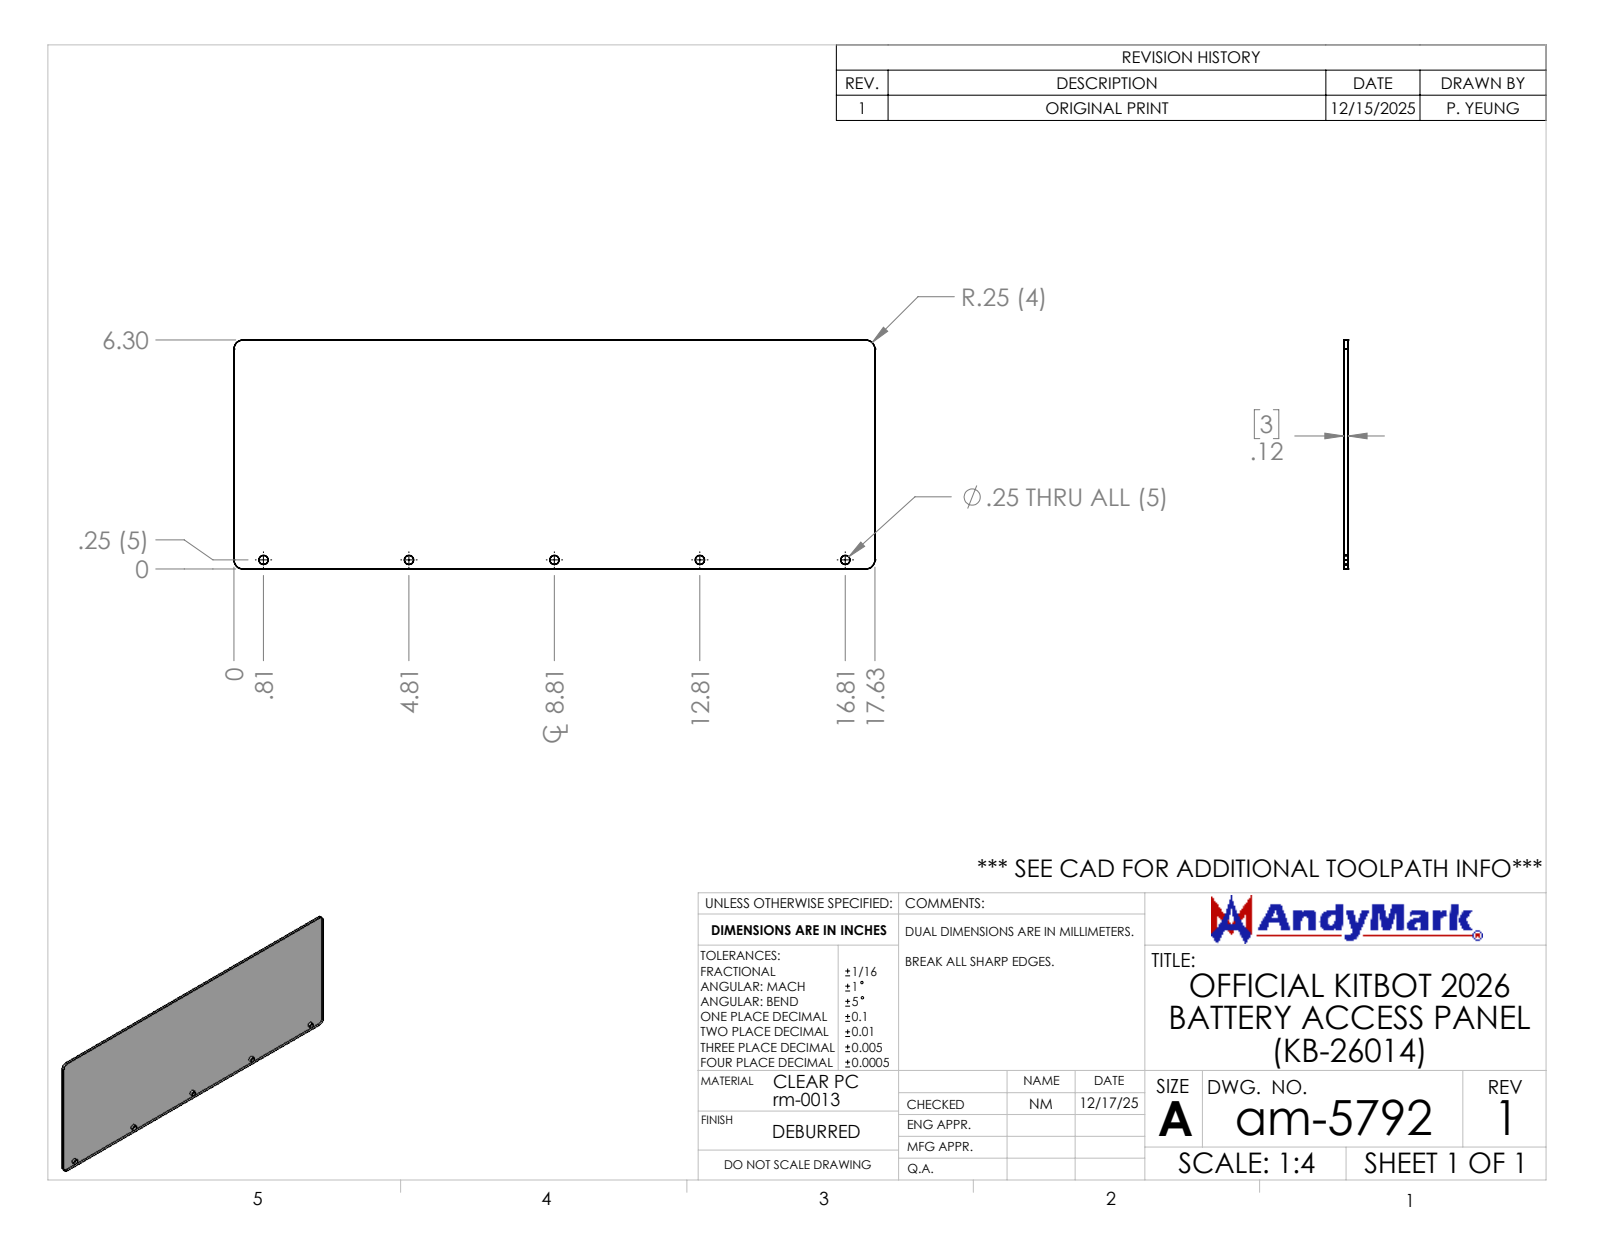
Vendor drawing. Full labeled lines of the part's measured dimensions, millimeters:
Part name (STEP PRODUCT): am-5792 Battery Access Panel (KB-26014)
STEP written by: SolidWorks 2024 (AUTOMOTIVE_DESIGN)
Units: millimetres
Bodies: 1 solid, 20 faces (6 planar, 14 cylindrical, 0 other)
Overall size (bounding box): 447.7 × 159.9 × 3
Volume: 214 200 mm³ · Surface area: 146 700 mm²
Round holes (diameter × count): ⌀6.4 ×5
Partial cylindrical surfaces — rounded edges, fillets, slot ends (radius × count): R6.4 ×4
Main face-to-face distances: 3, 159.9, 447.7
Hole centre spacings: 101.6, 203.2, 304.8, 406.4
